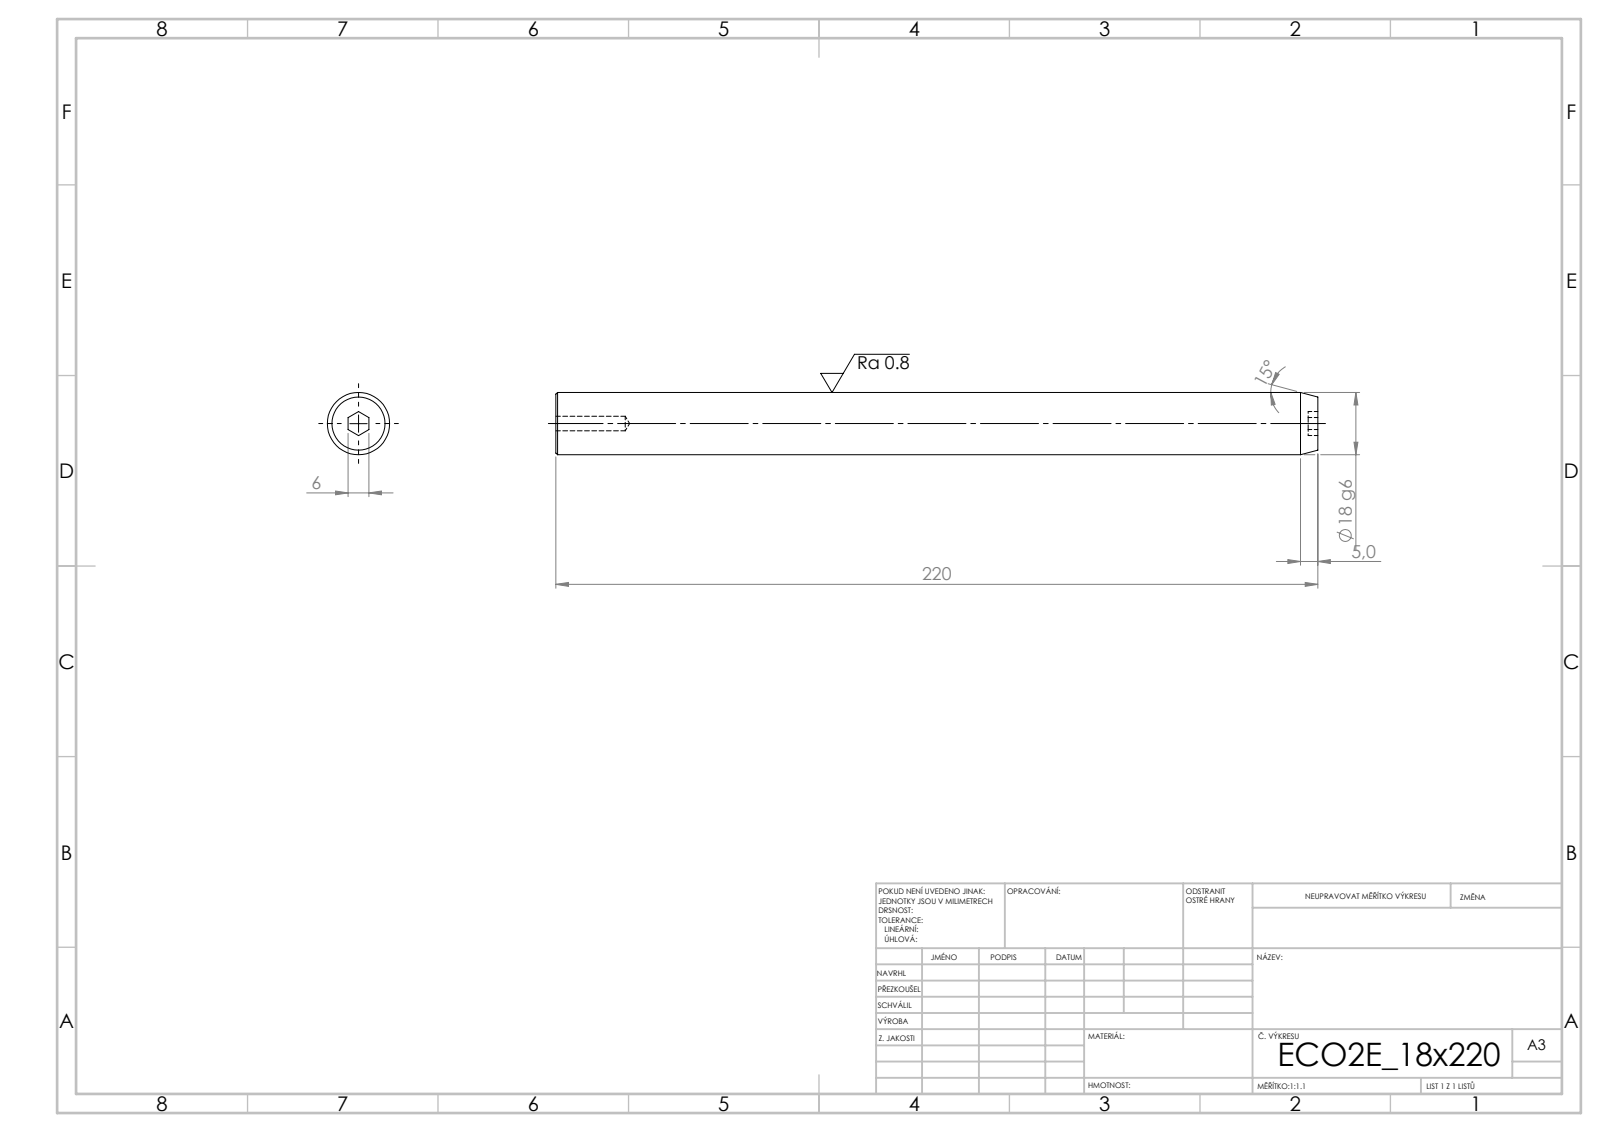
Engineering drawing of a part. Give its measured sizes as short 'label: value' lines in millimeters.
written by: SolidWorks 2019 (CONFIG_CONTROL_DESIGN)
unit: mm
bodies: 1 solid, 19 faces (9 planar, 4 cylindrical, 6 other)
size: 220 × 18 × 18
volume: 55 426 mm³; area: 13 175 mm²
holes: 1× ⌀4.2
bosses: 1× ⌀18
face distances: 220, 2.8, 217.2, 6
